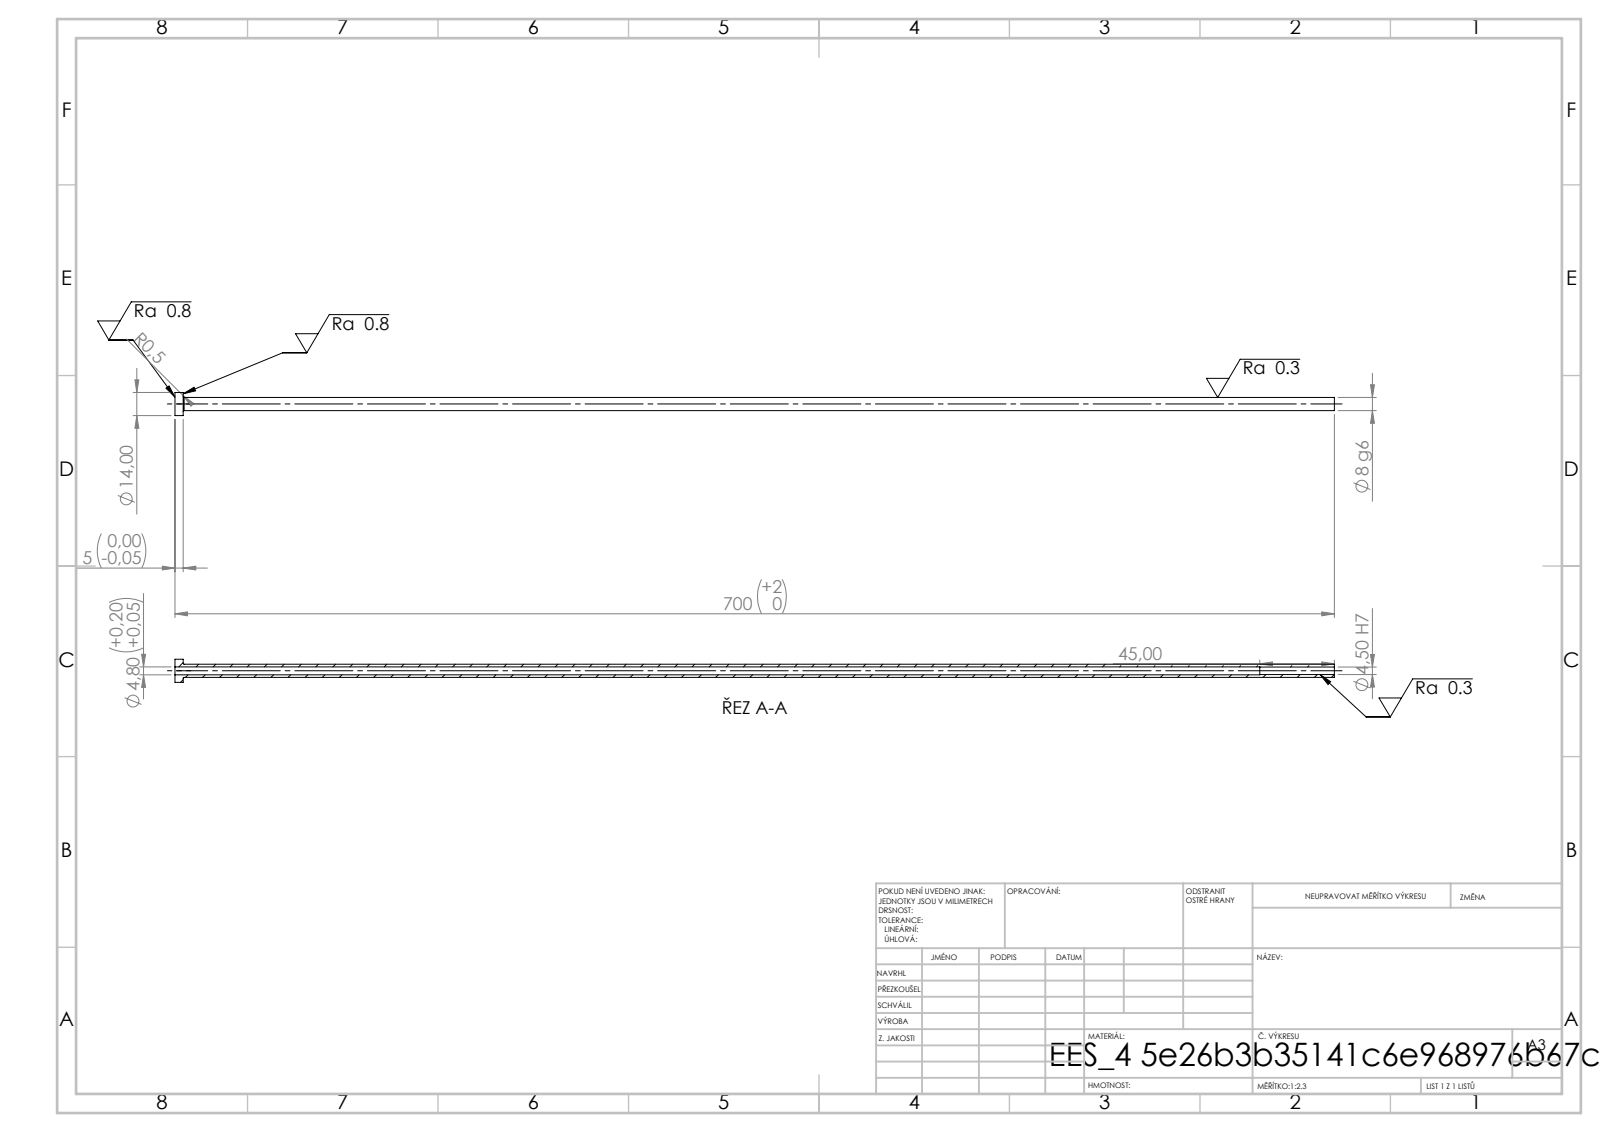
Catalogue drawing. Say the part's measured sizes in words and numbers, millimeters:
Its 3-D file was written by "SolidWorks 2019 (CONFIG_CONTROL_DESIGN)". It is 1 solid with 14 faces: 4 planar, 8 cylindrical and 2 other. Overall it measures 700 by 14 by 14 millimeters. Its volume is 23 137 cubic millimeters and its surface area 28 471 square millimeters. Round holes: 1 of diameter 4.5, 1 of diameter 4.8. Round bosses or shafts: 1 of diameter 14, 1 of diameter 8. The main face-to-face distances are 5, 700, 695, 655, 650, 45.
